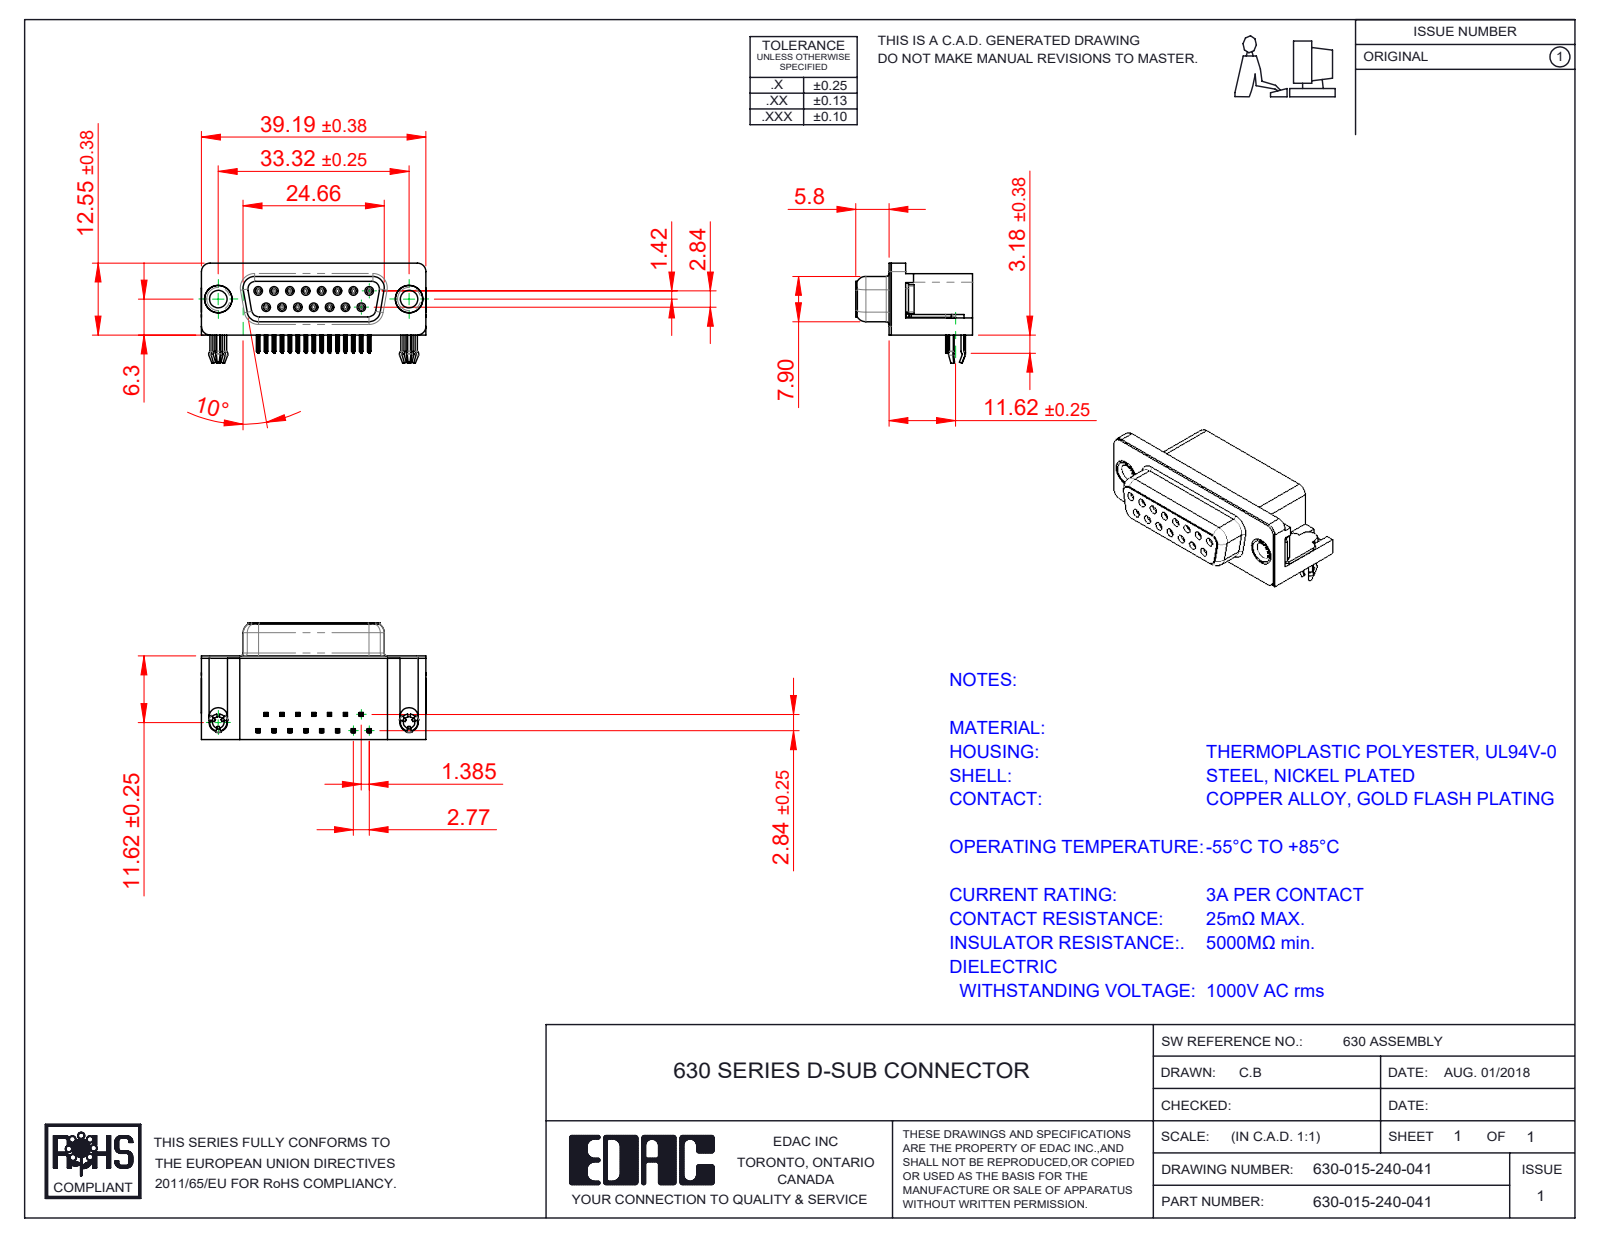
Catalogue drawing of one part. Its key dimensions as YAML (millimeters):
part_name: "630 Contact Top; 630 Contact Bottom; 630 3 Prong Board Lock; 630 Shell_15 Socket (+3 more)"
step_written_by: "SolidWorks 2020 (CONFIG_CONTROL_DESIGN)"
units: millimeters
bodies: {solids: 21, faces: 2489, planar: 1110, cylindrical: 593, other: 786}
overall_size: [39.22, 20.4, 17.48]
volume: 5856
surface_area: 7236
round_holes:
  - {diameter: 0.8, count: 15}
  - {diameter: 0.9, count: 15}
  - {diameter: 2, count: 2}
  - {diameter: 3.05, count: 2}
  - {diameter: 4, count: 2}
  - {diameter: 4.8, count: 2}
  - {diameter: 5, count: 2}
round_bosses_or_shafts:
  - {diameter: 1.2, count: 15}
  - {diameter: 4.9, count: 2}
  - {diameter: 4.75, count: 2}
  - {diameter: 3.85, count: 2}
  - {diameter: 3, count: 2}
partial_cylinders:
  - {radius: 0.1, count: 120}
  - {radius: 0.15, count: 60}
  - {radius: 0.35, count: 30}
  - {radius: 1, count: 18}
  - {radius: 0.34, count: 15}
  - {radius: 0.25, count: 12}
  - {radius: 1.35, count: 8}
  - {radius: 1.5, count: 8}
face_to_face_distances: [0.4, 14.2, 6.2, 10.35, 2.73, 14.6, 2.9, 3.18, 6.65, 9.38]
hole_center_spacings: [3.16, 2.77, 5.54, 5.03, 5.04, 7.48, 7.49, 8.31]
